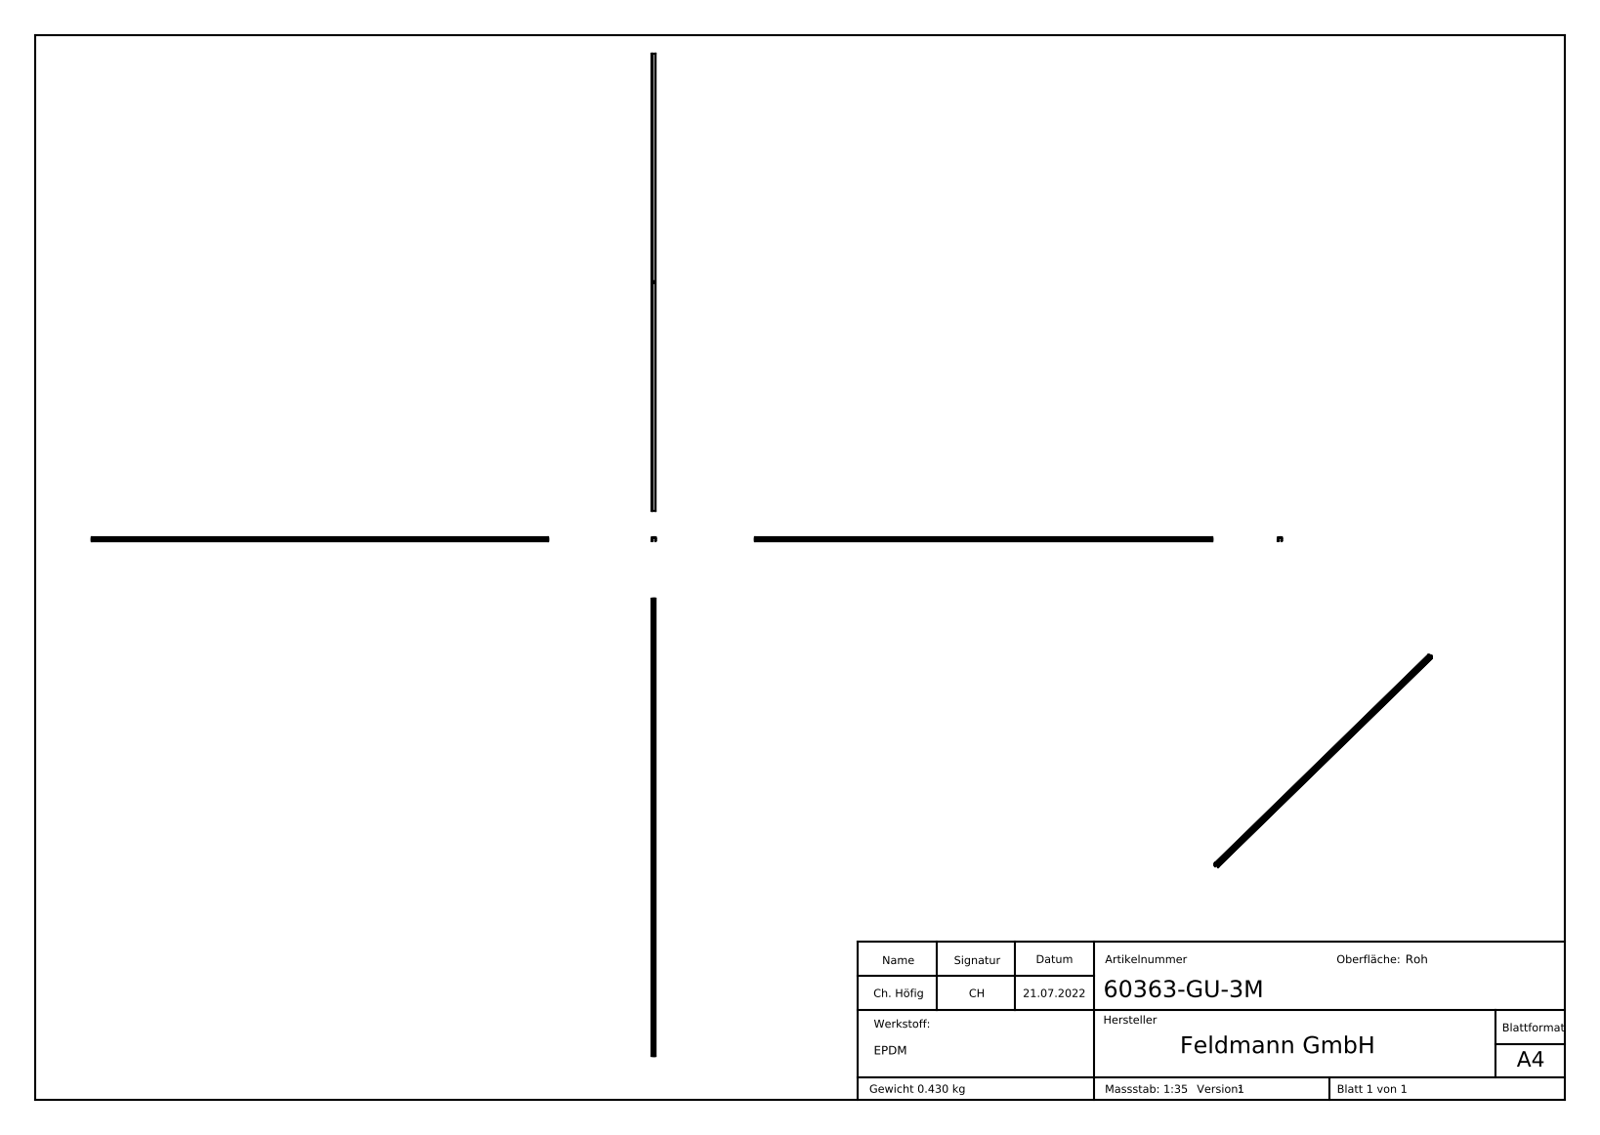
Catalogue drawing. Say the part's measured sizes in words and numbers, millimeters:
The part is named "60363-GU-3M". Its 3-D file was written by "SolidWorks 2018 (CONFIG_CONTROL_DESIGN)". It is 1 solid with 381 faces: 188 planar, 40 cylindrical and 153 other. Overall it measures 3000 by 25.2 by 23 millimeters. Its volume is 364 255 cubic millimeters and its surface area 502 639 square millimeters. Partial cylindrical surfaces (rounded edges, fillets, slot ends): 22 of radius 0.4, 14 of radius 0.3, 2 of radius 1, 2 of radius 1.5. The main face-to-face distances are 1.3, 23.1, 1.5, 3.5, 21.8, 24.4, 5, 2, 1.56, 1.55.
